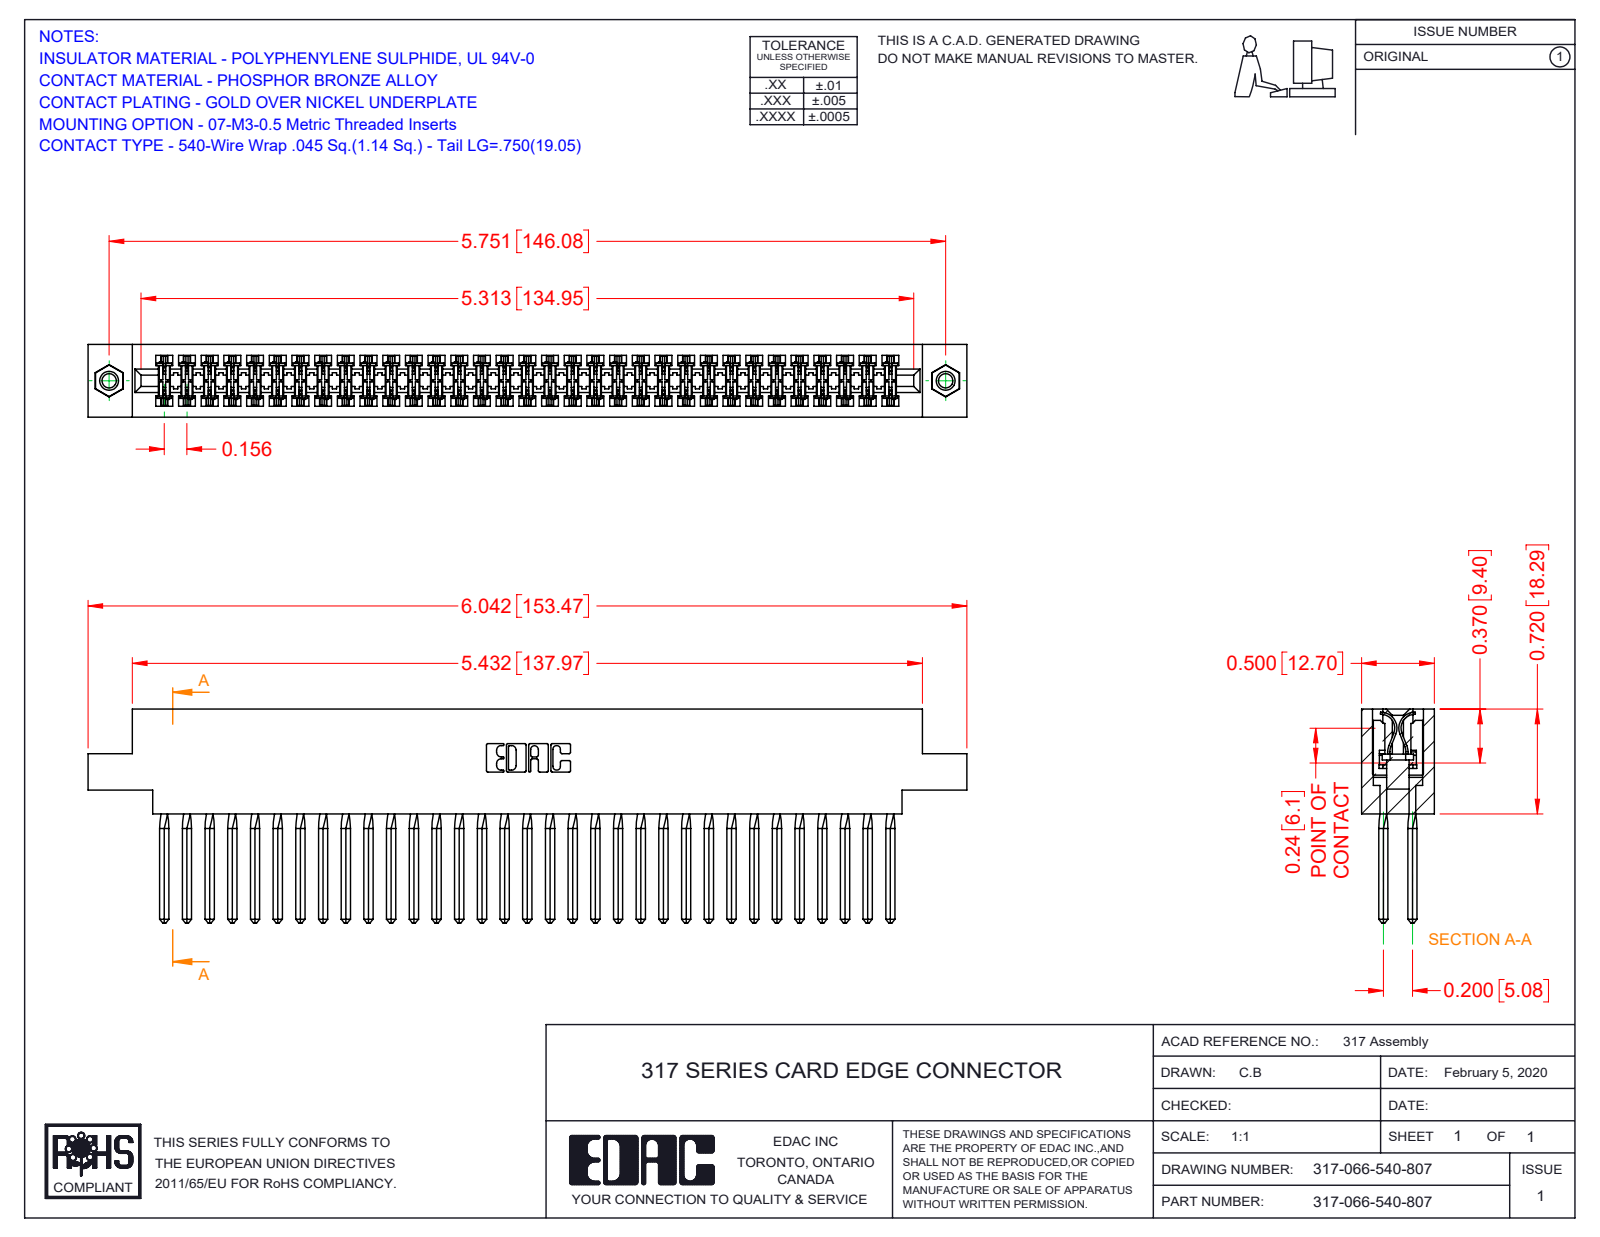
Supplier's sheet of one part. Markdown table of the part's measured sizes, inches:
| quantity | value |
| --- | --- |
| part name | 345-250-001_345-250-005-103; 317-290-001_540; 317 Part_.156 Dia - TI; 317-066-540-807 |
| STEP written by | SolidWorks 2016 (CONFIG_CONTROL_DESIGN) |
| units | inches |
| bodies | 69 solids, 6036 faces (4908 planar, 848 cylindrical, 280 other) |
| overall size | 6.042 × 1.47 × 0.5 |
| volume | 1.552 in³ |
| surface area | 58.32 in² |
| round holes (diameter × count) | 0.098 × 2, 0.125 × 2, 0.156 × 2 |
| round bosses / shafts (diameter × count) | 0.155 × 2 |
| partial cylindrical surfaces (radius × count) | 0.015 × 132, 0.01 × 22, 0.007 × 6, 0.031 × 6, 0.026 × 3, 0.095 × 2, 0.1 × 2, 0.11 × 2 |
| main face-to-face distances | 0.5, 0.075, 0.425, 0.35, 0.11, 0.195, 0.094, 0.2, 0.115, 0.131 |
| hole center spacings | 5.751 |
